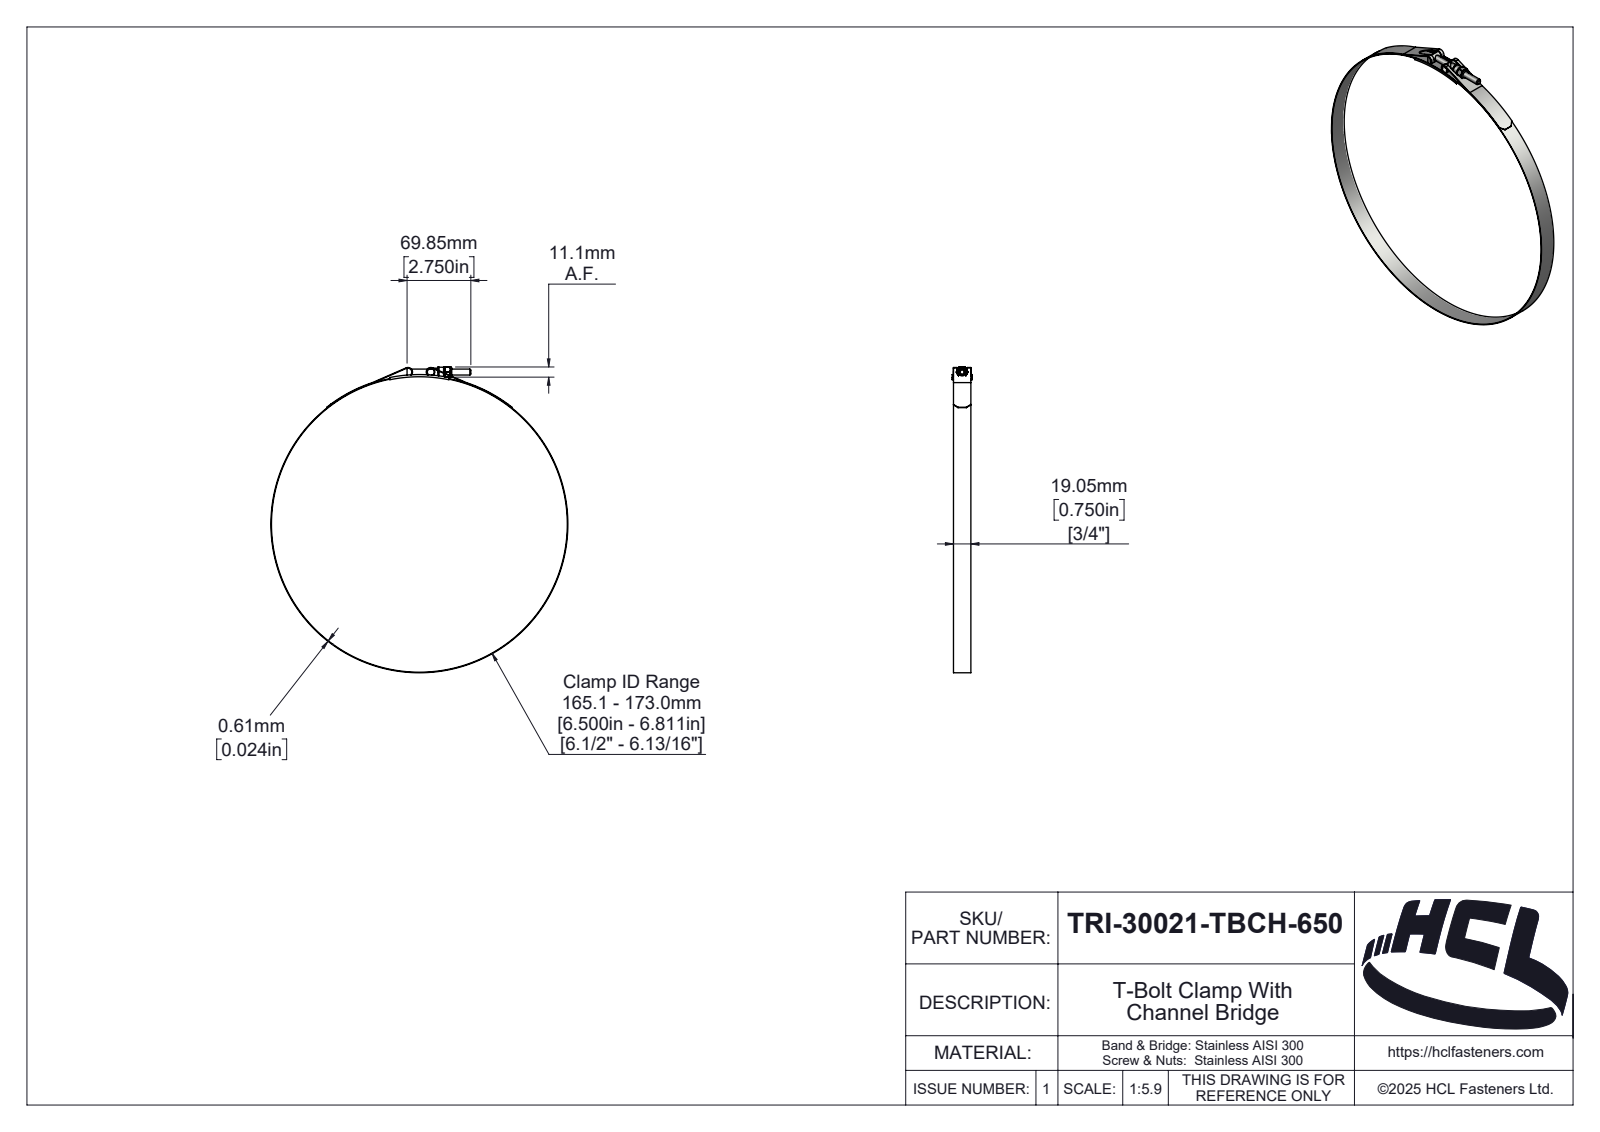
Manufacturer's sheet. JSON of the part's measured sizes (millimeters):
{"part_name": "TRI-30021-TBCH-650", "step_written_by": "SolidWorks 2025 (AUTOMOTIVE_DESIGN)", "units": "millimeters", "bodies": {"solids": 6, "faces": 330, "planar": 46, "cylindrical": 122, "other": 162}, "overall_size": [334.86, 325.22, 22], "volume_mm3": 18933, "surface_area_mm2": 54418, "round_holes": [[5.4, 1], [6.35, 1], [6.5, 1], [7.58, 1], [324, 1]], "round_bosses_or_shafts": [[8.58, 2], [325.22, 1], [10.58, 1]], "partial_cylinders_radius": [[0.39, 6], [0.5, 2], [4.39, 2], [5, 2], [0.59, 1], [2.42, 1], [3.03, 1], [3.19, 1]], "face_to_face_distances": [0.61, 19.06, 1.47, 20.53, 21.39, 0.86, 19.92, 22, 0.74, 20.78], "hole_center_spacings": [167]}
